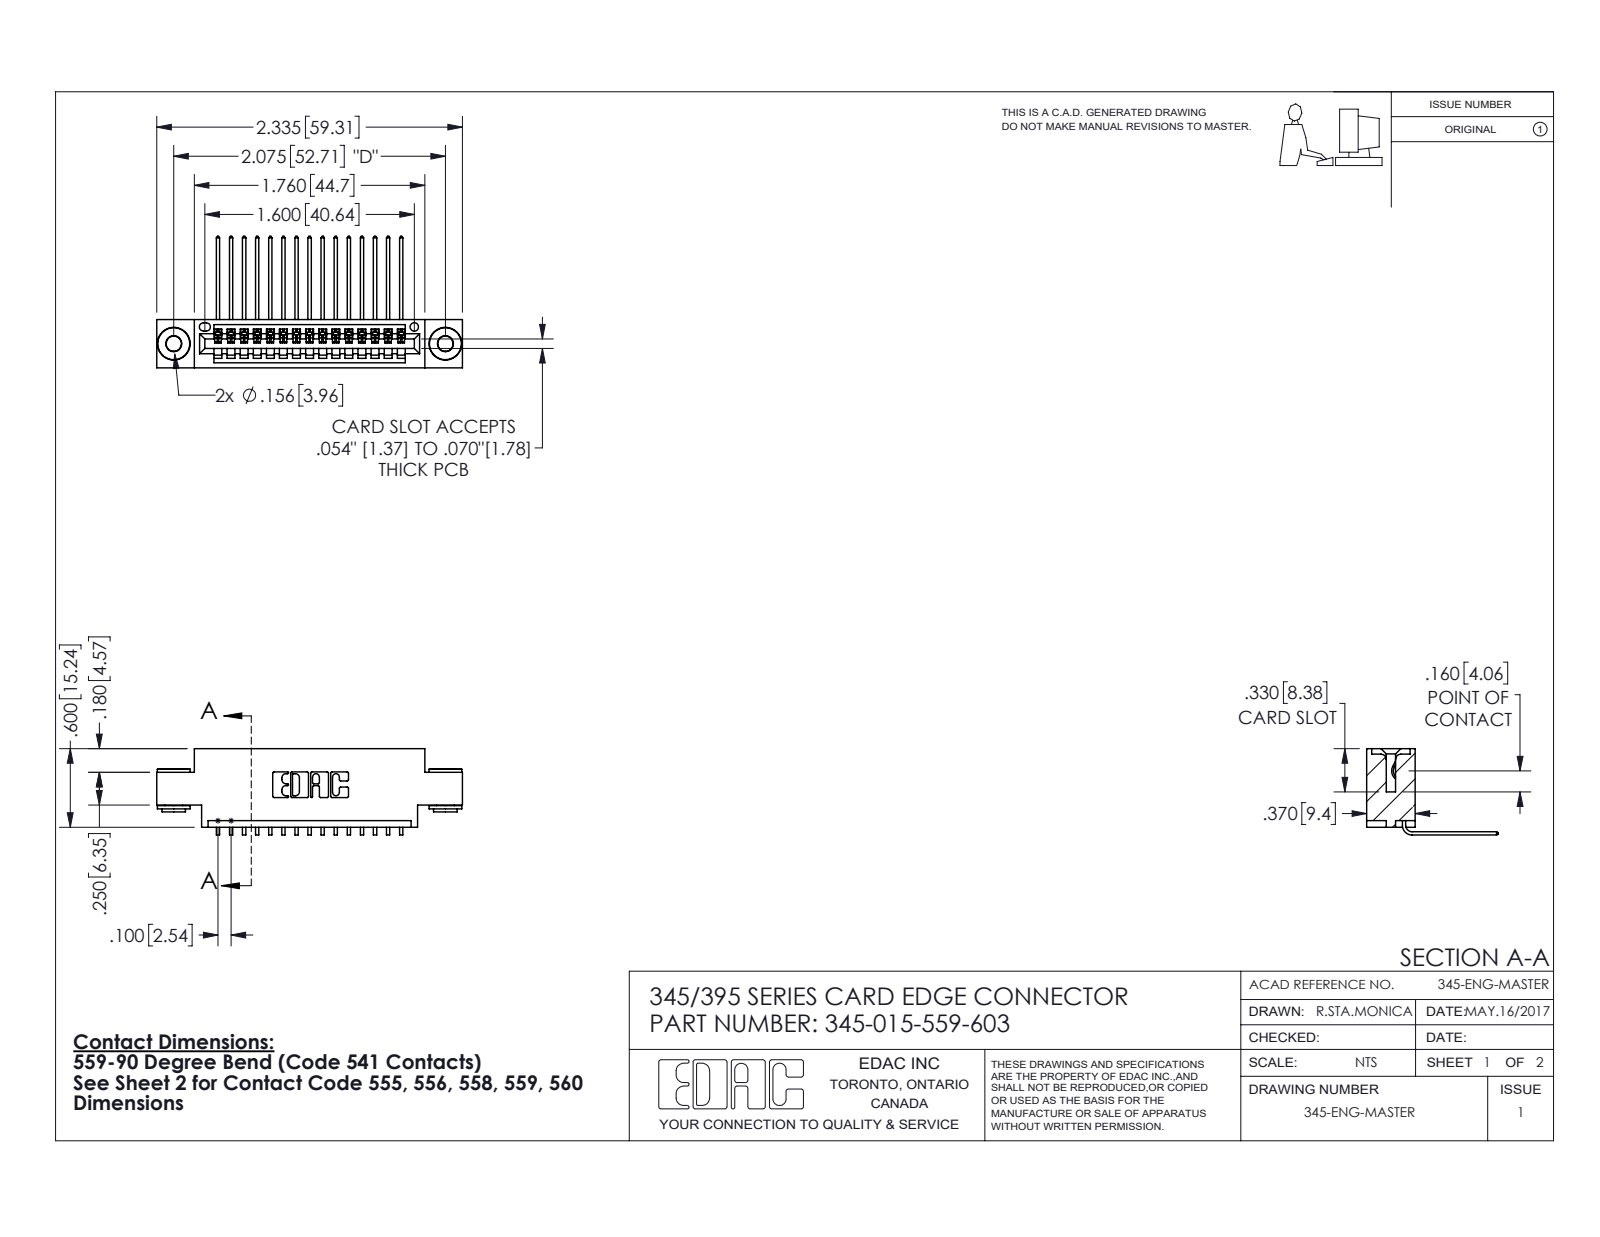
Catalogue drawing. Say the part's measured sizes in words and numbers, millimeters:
The part is named "345-015-559-603; 345-292-001_558 559 Tail - 1; 345 Part_0.170 Offset - 0.156 Dia-TH; 345-250-002_345-250-002-102". Its 3-D file was written by "SolidWorks 2016 (CONFIG_CONTROL_DESIGN)". It is 18 solids with 1068 faces: 724 planar, 336 cylindrical and 8 other. Overall it measures 59.3 by 25.5 by 16.7 millimeters. Its volume is 5 370 cubic millimeters and its surface area 7 400 square millimeters. Round holes: 2 of diameter 2.9, 2 of diameter 4, 1 of diameter 1.6. Round bosses or shafts: 2 of diameter 6.4, 2 of diameter 4.6, 2 of diameter 3.5. Partial cylindrical surfaces (rounded edges, fillets, slot ends): 30 of radius 0.2, 22 of radius 0.3, 6 of radius 0.2, 6 of radius 0.8, 3 of radius 0.7, 2 of radius 0.8, 2 of radius 1, 1 of radius 0.4. The main face-to-face distances are 9.4, 1.8, 7.6, 5.1, 2.5, 6.9, 0.6, 2.5, 4.4, 5.7. The hole center spacings are 6.9, 46.8, 52.7.
